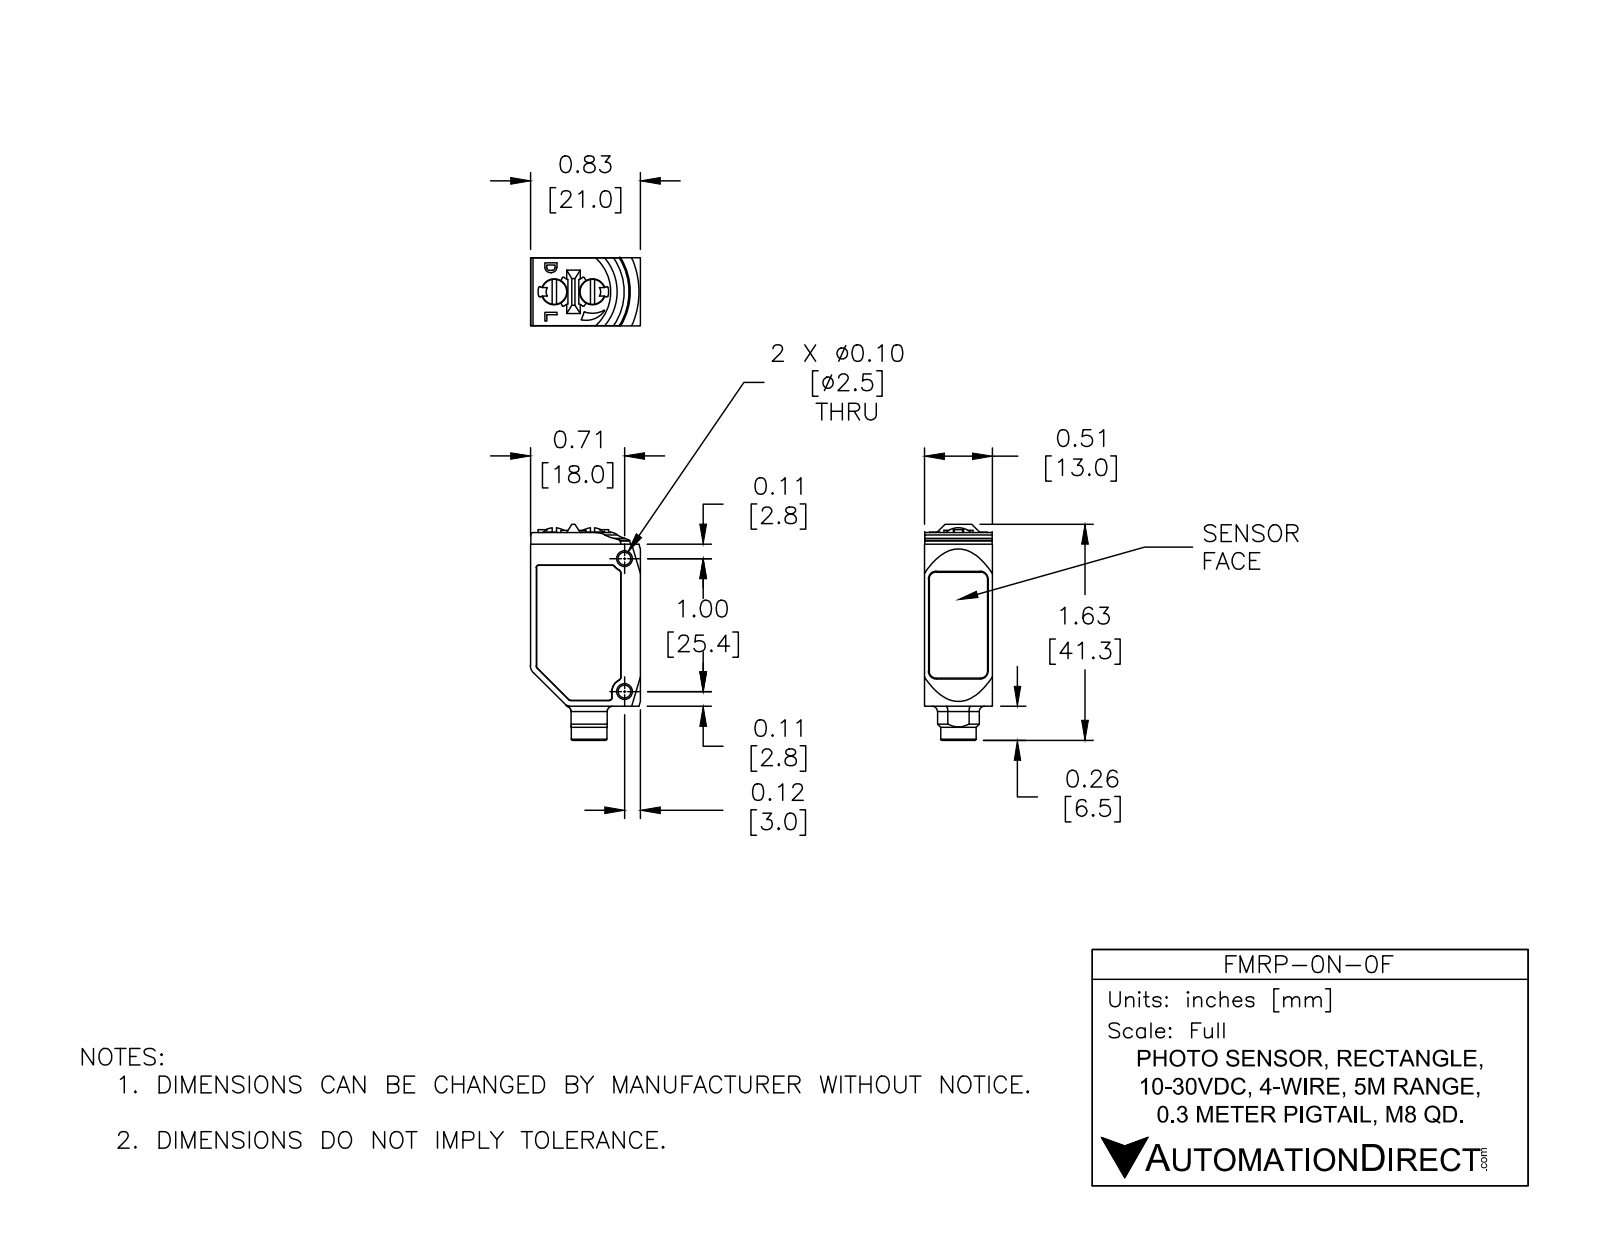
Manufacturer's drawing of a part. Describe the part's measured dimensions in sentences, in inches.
The part is named "FMRP-0N-0F". Its 3-D file was written by "SolidWorks 2017 (AUTOMOTIVE_DESIGN)". It is 1 solid with 197 faces: 89 planar, 79 cylindrical and 29 other. Overall it measures 1.626 by 0.827 by 0.512 inches. Its volume is 0.527 cubic inches and its surface area 5.26 square inches. Round holes: 2 of diameter 0.097, 2 of diameter 0.197, 1 of diameter 0.228. Round bosses or shafts: 2 of diameter 0.189, 1 of diameter 0.267. Partial cylindrical surfaces (rounded edges, fillets, slot ends): 7 of radius 0.018, 7 of radius 0.02, 5 of radius 0.039, 4 of radius 0.008, 4 of radius 0.01, 4 of radius 0.051, 4 of radius 0.059, 3 of radius 0.004. The main face-to-face distances are 0.512, 0.827, 1.307, 0.51, 0.031, 0.48, 0.037, 0.035, 0.474, 0.03. The hole center spacings are 0.026, 0.262, 0.287, 1.
